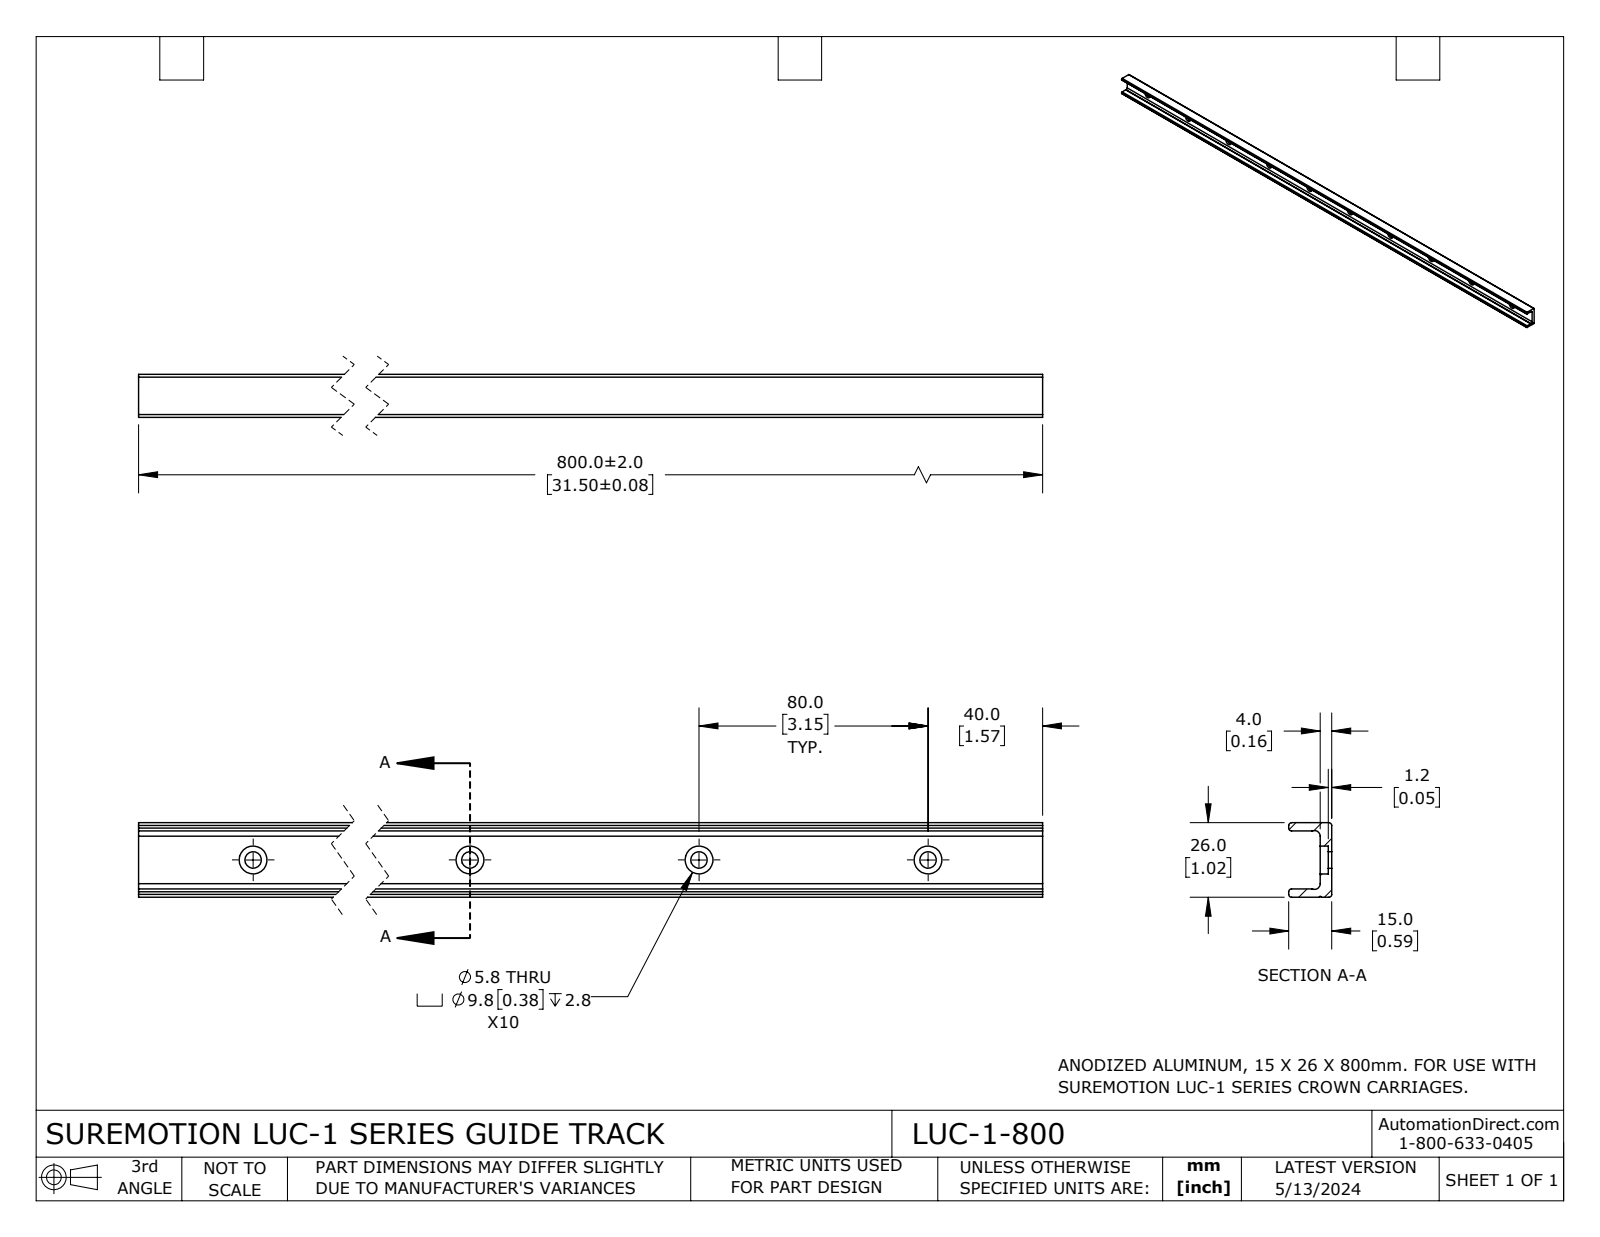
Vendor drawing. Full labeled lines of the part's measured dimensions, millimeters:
Part name (STEP PRODUCT): LUC-1-800
STEP written by: SolidWorks 2023 (CONFIG_CONTROL_DESIGN)
Units: millimetres
Bodies: 1 solid, 72 faces (21 planar, 51 cylindrical, 0 other)
Overall size (bounding box): 800 × 26.01 × 15.01
Volume: 131 580 mm³ · Surface area: 81 285 mm²
Round holes (diameter × count): ⌀5.79 ×10, ⌀9.75 ×10
Partial cylindrical surfaces — rounded edges, fillets, slot ends (radius × count): R0.99 ×8, R1.98 ×2, R0.33 ×1
Main face-to-face distances: 4.01, 2.9, 23.12, 26.02, 20.22, 15.02, 11.01, 1.21, 2.8, 13.81
Hole centre spacings: 80, 160, 240, 320, 400, 480, 560, 640
